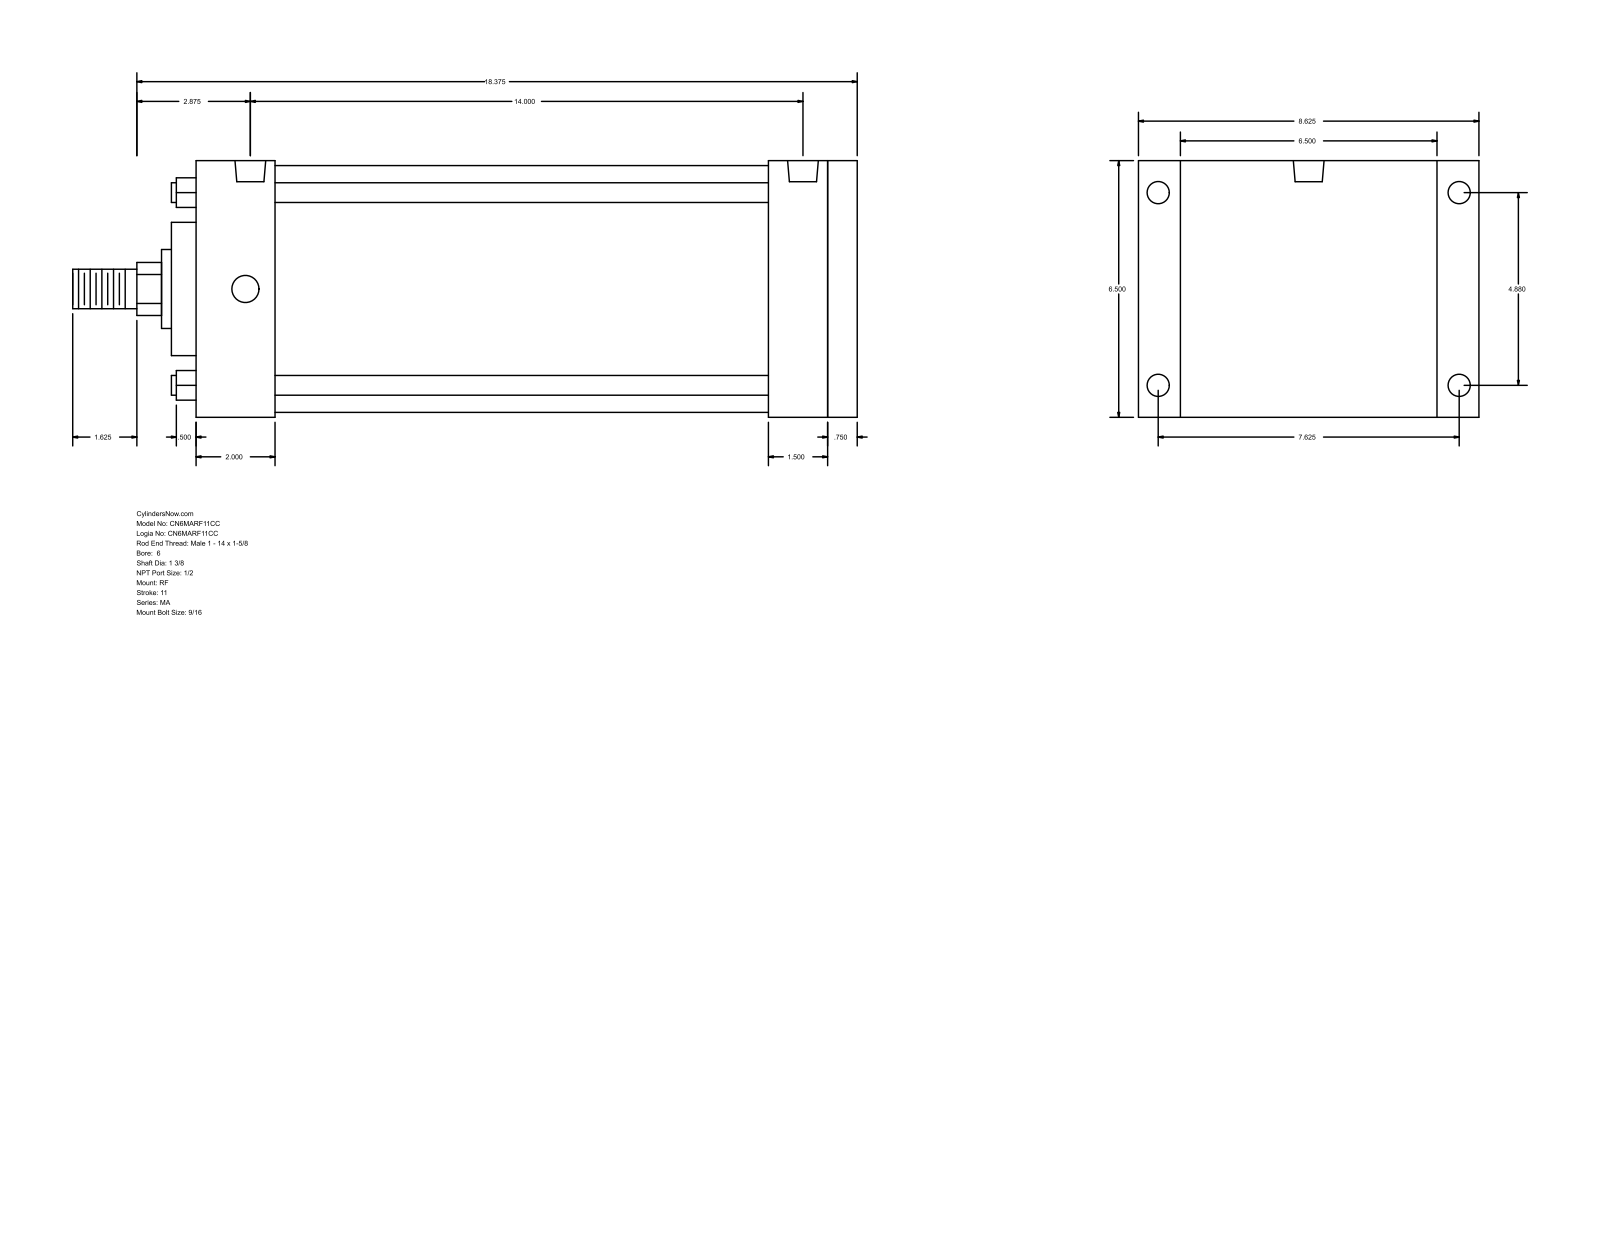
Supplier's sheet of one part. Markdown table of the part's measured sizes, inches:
| quantity | value |
| --- | --- |
| part name | MA_RF__0600_1.375 |
| STEP written by | GSSL Pune (CONFIG_CONTROL_DESIGN) |
| units | inches |
| bodies | 0 solids, 94 faces (65 planar, 29 cylindrical, 0 other) |
| overall size | 20 × 8.625 × 6.5 |
| round holes (diameter × count) | 0.563 × 4, 0.687 × 4, 0.778 × 2 |
| round bosses / shafts (diameter × count) | 0.5 × 4, 6.25 × 1, 3.375 × 1, 2 × 1, 1.375 × 1, 1 × 1 |
| partial cylindrical surfaces (radius × count) | 0.672 × 1 |
| main face-to-face distances | 6.5, 16.875, 0.75, 16.125, 2, 14.125, 14.875, 14.625, 12.625, 1.5 |
| hole center spacings | 4.88, 7.625, 9.053, 14.125, 0.125, 14 |
